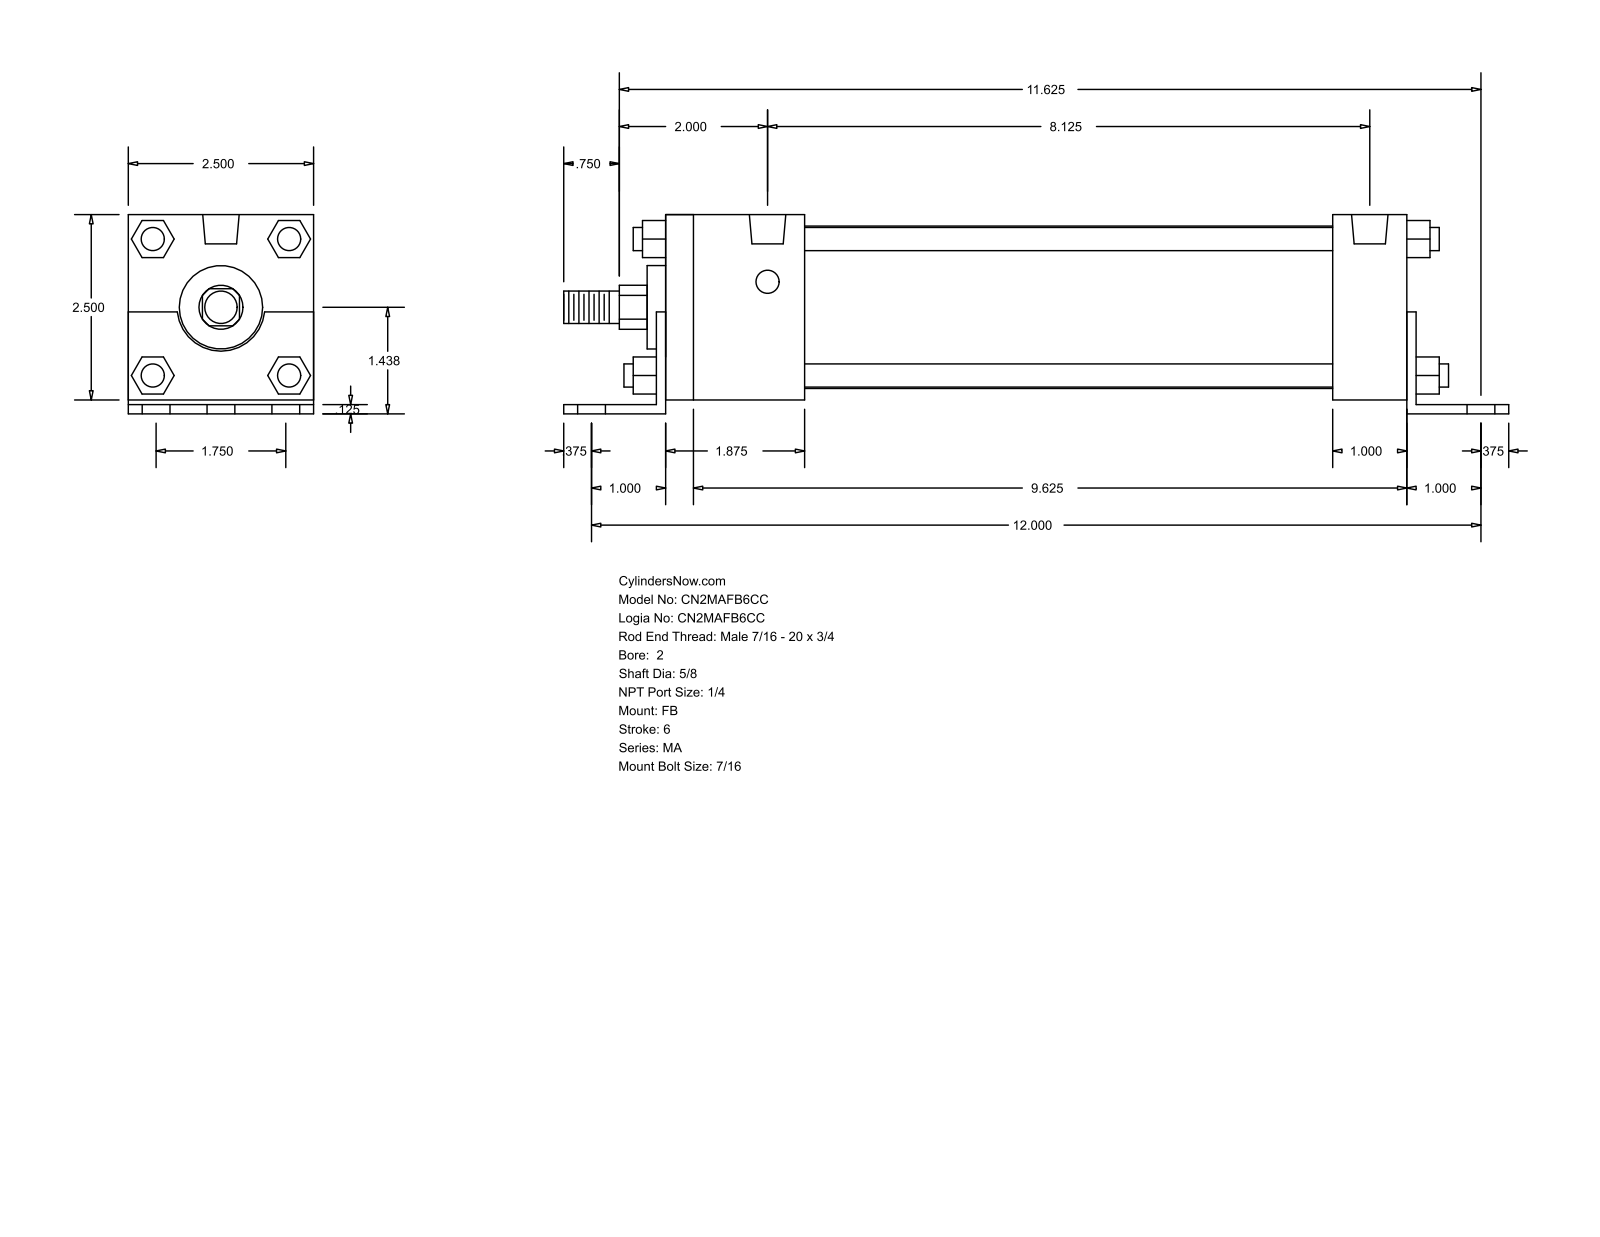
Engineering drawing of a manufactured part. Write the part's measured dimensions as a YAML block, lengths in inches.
part_name: "MA_FB__0200_0.625"
step_written_by: "GSSL Pune (CONFIG_CONTROL_DESIGN)"
units: inches
bodies: {solids: 0, faces: 140, planar: 105, cylindrical: 35, other: 0}
overall_size: [12.75, 2.687, 2.5]
round_holes:
  - {diameter: 0.437, count: 6}
  - {diameter: 0.313, count: 4}
  - {diameter: 0.492, count: 2}
round_bosses_or_shafts:
  - {diameter: 0.313, count: 4}
  - {diameter: 2.19, count: 1}
  - {diameter: 1.125, count: 1}
  - {diameter: 0.625, count: 1}
  - {diameter: 0.437, count: 1}
partial_cylinders:
  - {radius: 0.297, count: 1}
  - {radius: 0.593, count: 1}
face_to_face_distances: [2.5, 0.125, 0.187, 2.687, 0.063, 2.563, 10.25, 0.125, 10, 10.125]
hole_center_spacings: [0.875, 12.032, 12, 1.736, 1.75, 2.531, 8.125, 9.665]
